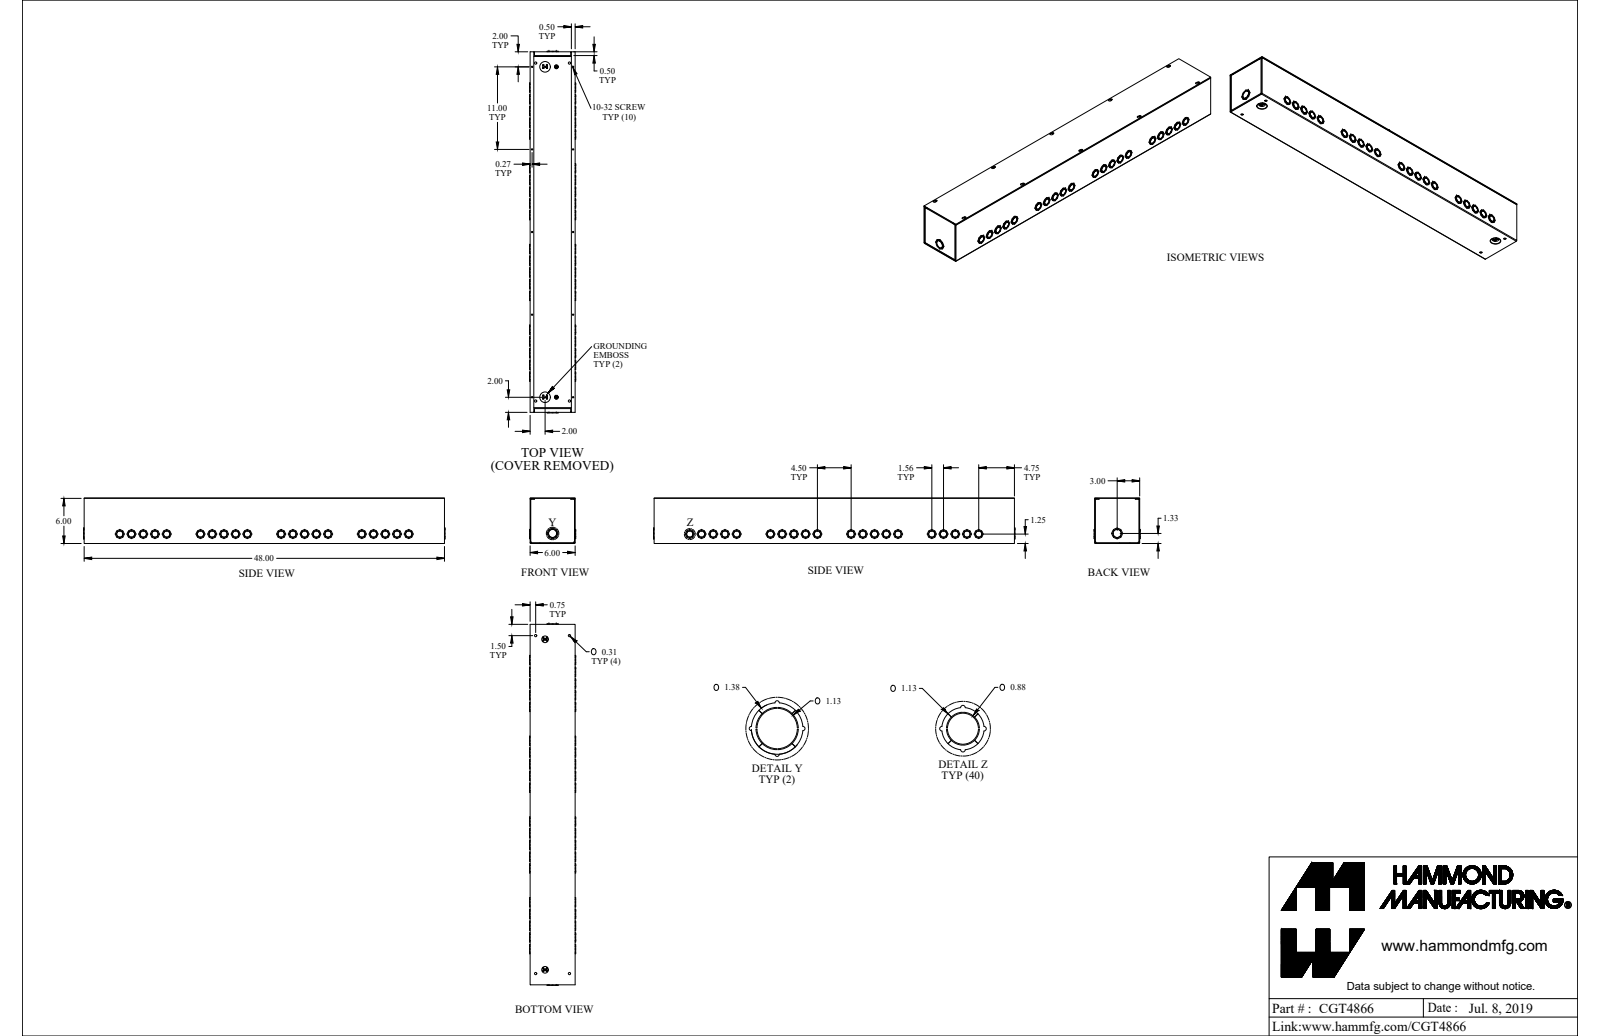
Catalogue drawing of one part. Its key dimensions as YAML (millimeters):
part_name: "CGT4866"
step_written_by: "SolidWorks 2021 (AUTOMOTIVE_DESIGN)"
units: millimeters
bodies: {solids: 6, faces: 2038, planar: 930, cylindrical: 1094, other: 14}
overall_size: [1222.9, 158.7, 156.1]
volume: 1331000
surface_area: 1677000
round_holes:
  - {diameter: 22.2, count: 20}
  - {diameter: 4.3, count: 12}
  - {diameter: 7.9, count: 4}
  - {diameter: 12.7, count: 2}
  - {diameter: 28.6, count: 1}
round_bosses_or_shafts:
  - {diameter: 28.6, count: 20}
  - {diameter: 21, count: 20}
  - {diameter: 12.5, count: 2}
  - {diameter: 9.5, count: 2}
  - {diameter: 7.2, count: 2}
  - {diameter: 4.8, count: 2}
  - {diameter: 34.9, count: 1}
  - {diameter: 27.3, count: 1}
partial_cylinders:
  - {radius: 1.6, count: 80}
  - {radius: 3.2, count: 10}
  - {radius: 5.2, count: 10}
  - {radius: 0.9, count: 8}
  - {radius: 1.4, count: 8}
  - {radius: 2.7, count: 8}
  - {radius: 0.7, count: 4}
  - {radius: 1.4, count: 4}
face_to_face_distances: [1.4, 151, 152.4, 1.8, 149.5, 154.2, 152.8, 3.3, 1217.4, 1219.2]
hole_center_spacings: [273, 79.3, 39.7, 39.7, 193.6, 233.3, 279.4, 311.9]
